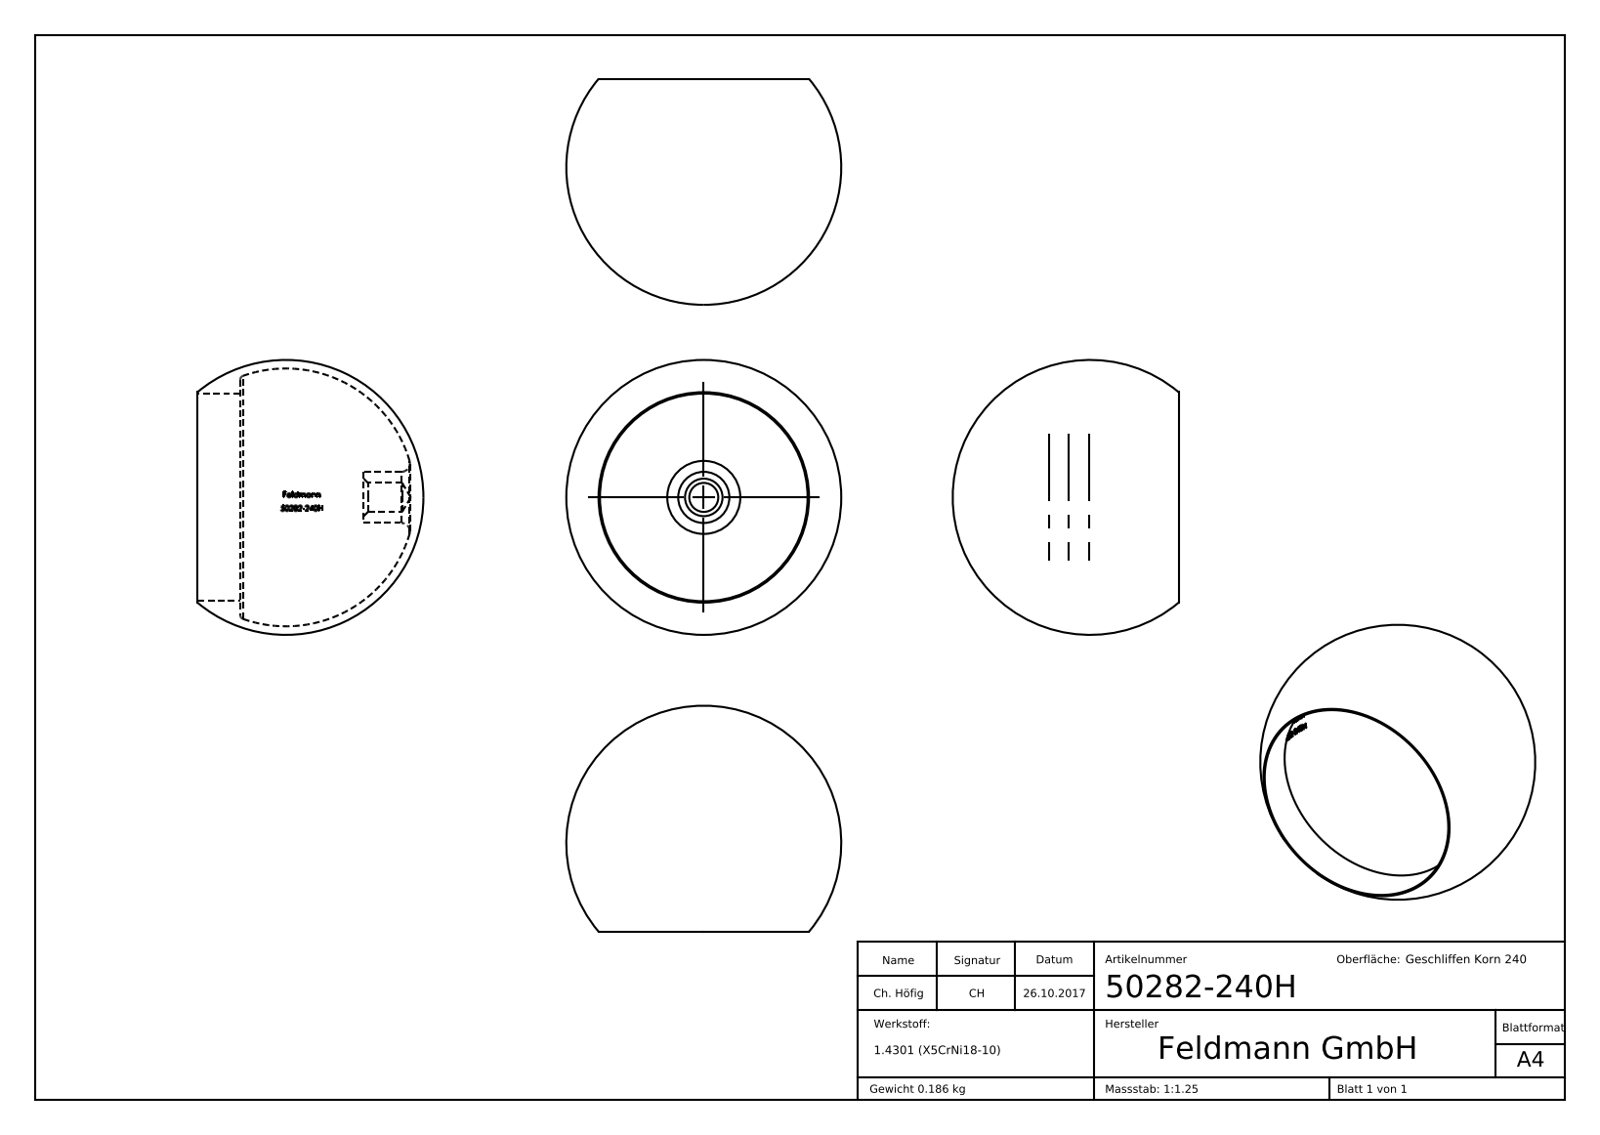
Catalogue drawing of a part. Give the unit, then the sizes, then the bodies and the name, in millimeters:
Units: millimetres
Overall size (bounding box): 64.5 × 64.5 × 53
Round holes (diameter × count): ⌀6.8 ×1, ⌀48.7 ×1
Round bosses / shafts (diameter × count): ⌀12 ×1
Main face-to-face distances: 10, 29, 39, 5.73, 1.25, 3.2, 1.37, 2.02, 6.98, 6.18
Volume: 23 530 mm³ · Surface area: 21 303 mm²
Bodies: 1 solid, 264 faces (110 planar, 6 cylindrical, 148 other)
Part name (STEP PRODUCT): 50282-240H
STEP written by: SolidWorks 2015 (CONFIG_CONTROL_DESIGN)
